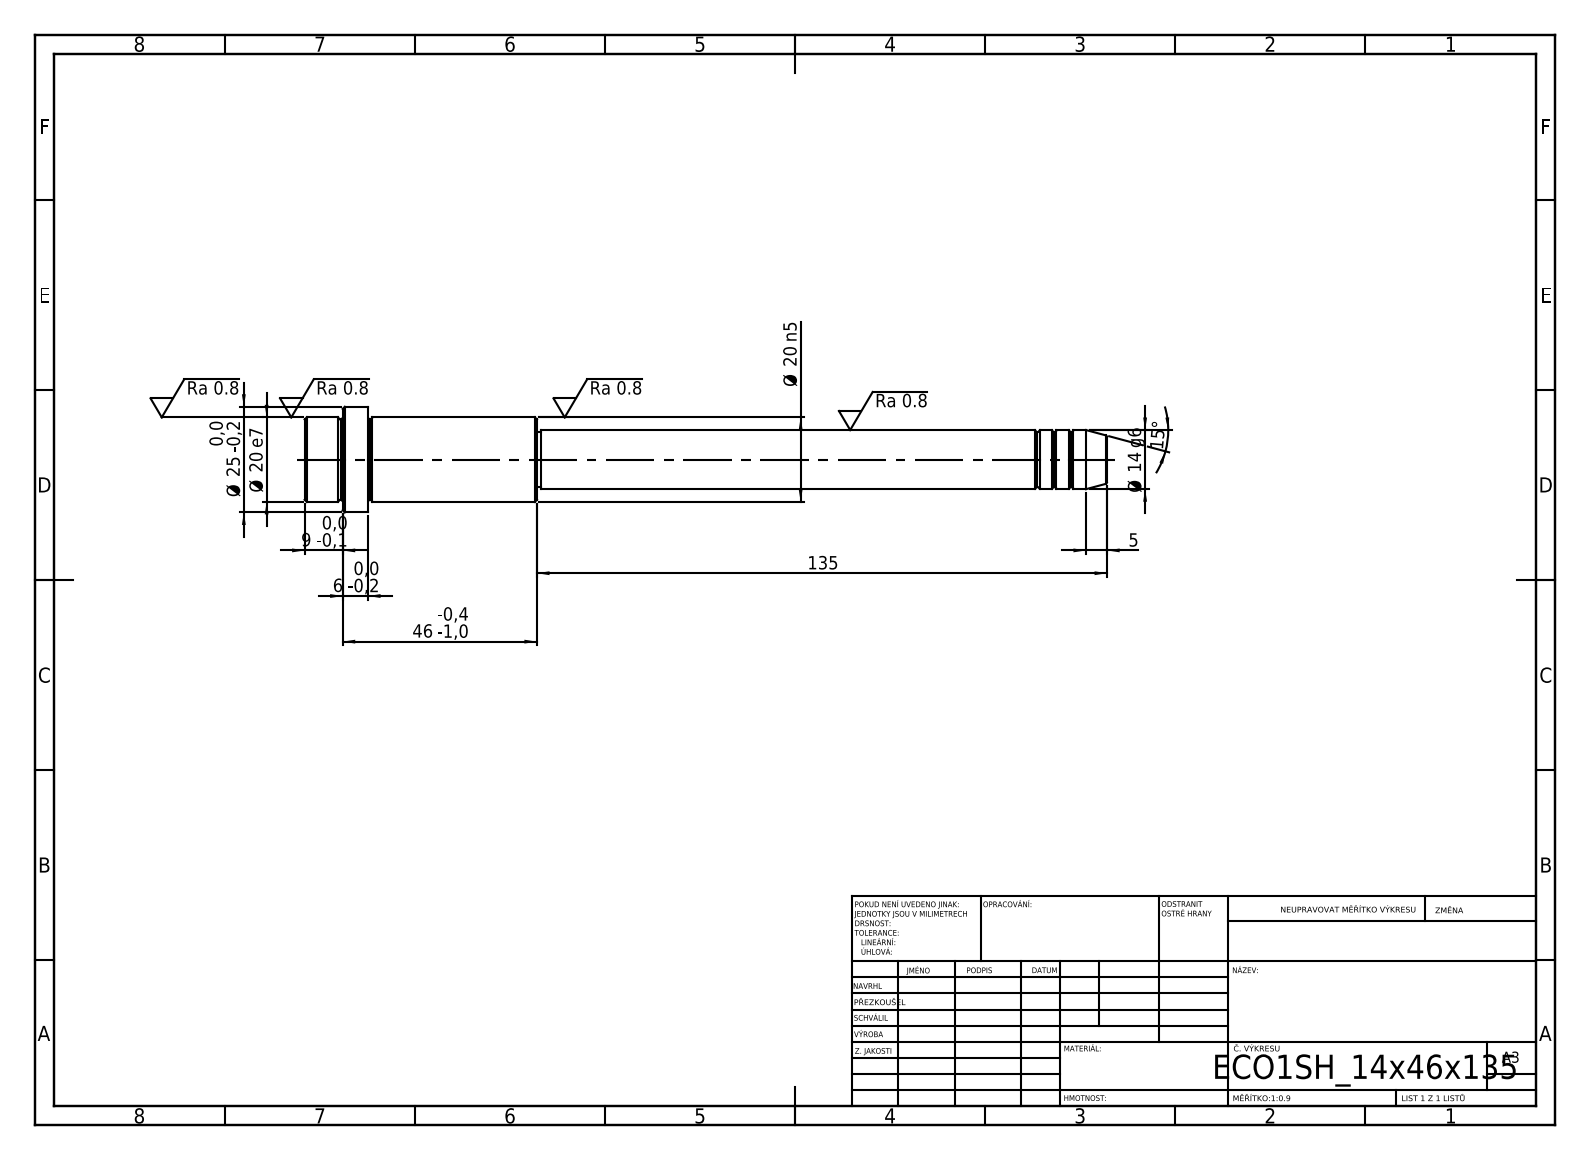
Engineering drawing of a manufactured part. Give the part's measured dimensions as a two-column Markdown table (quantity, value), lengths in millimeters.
| quantity | value |
| --- | --- |
| STEP written by | SolidWorks 2019 (CONFIG_CONTROL_DESIGN) |
| units | millimeters |
| bodies | 1 solid, 52 faces (6 planar, 16 cylindrical, 30 other) |
| overall size | 190 × 25 × 25 |
| volume | 38 837 mm³ |
| surface area | 10 508 mm² |
| round bosses / shafts (diameter × count) | 25 × 1, 20 × 1, 14 × 1, 13 × 1 |
| main face-to-face distances | 15, 40, 55, 46, 6, 9, 135, 175, 181, 190 |
